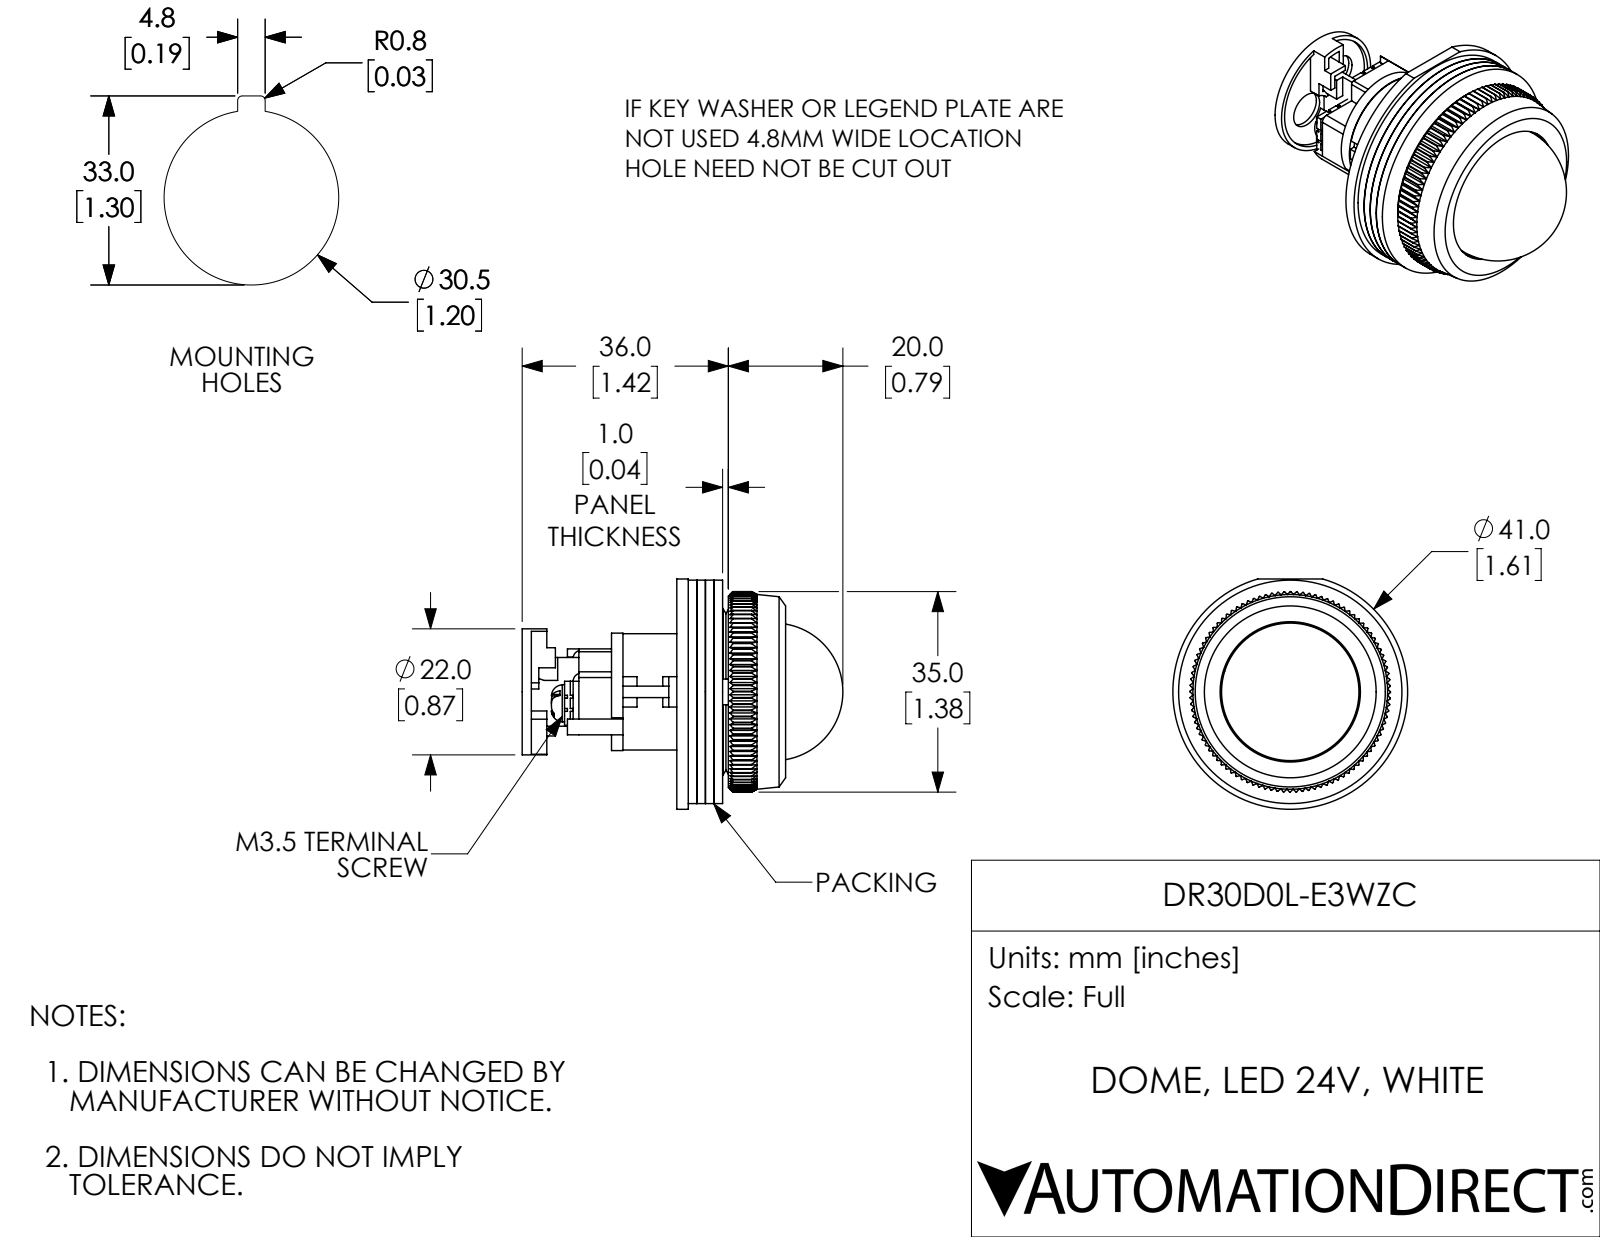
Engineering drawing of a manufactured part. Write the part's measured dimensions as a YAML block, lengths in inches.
part_name: "DR30D0L-E3WZC"
step_written_by: "SolidWorks 2017 (AUTOMOTIVE_DESIGN)"
units: inches
bodies: {solids: 16, faces: 1350, planar: 770, cylindrical: 336, other: 244}
overall_size: [2.203, 1.614, 1.583]
volume: 1.045
surface_area: 37.94
round_holes:
  - {diameter: 0.118, count: 2}
  - {diameter: 0.138, count: 2}
  - {diameter: 0.252, count: 2}
  - {diameter: 0.362, count: 1}
  - {diameter: 0.461, count: 1}
  - {diameter: 0.543, count: 1}
  - {diameter: 0.563, count: 1}
  - {diameter: 0.583, count: 1}
  - {diameter: 0.63, count: 1}
  - {diameter: 0.709, count: 1}
  - {diameter: 0.72, count: 1}
  - {diameter: 0.787, count: 1}
round_bosses_or_shafts:
  - {diameter: 0.063, count: 2}
  - {diameter: 1.614, count: 1}
  - {diameter: 1.535, count: 1}
  - {diameter: 1.16, count: 1}
  - {diameter: 0.945, count: 1}
  - {diameter: 0.858, count: 1}
  - {diameter: 0.819, count: 1}
  - {diameter: 0.799, count: 1}
partial_cylinders:
  - {radius: 0.059, count: 8}
  - {radius: 0.01, count: 5}
  - {radius: 0.022, count: 5}
  - {radius: 0.016, count: 4}
  - {radius: 0.055, count: 4}
  - {radius: 0.02, count: 2}
  - {radius: 0.039, count: 2}
  - {radius: 0.146, count: 2}
face_to_face_distances: [0.059, 0.118, 0.177, 0.039, 0.197, 0.079, 0.315, 0.256, 0.098, 0.236]
hole_center_spacings: [0.176, 0.185, 0.361, 0.352, 0.37]
